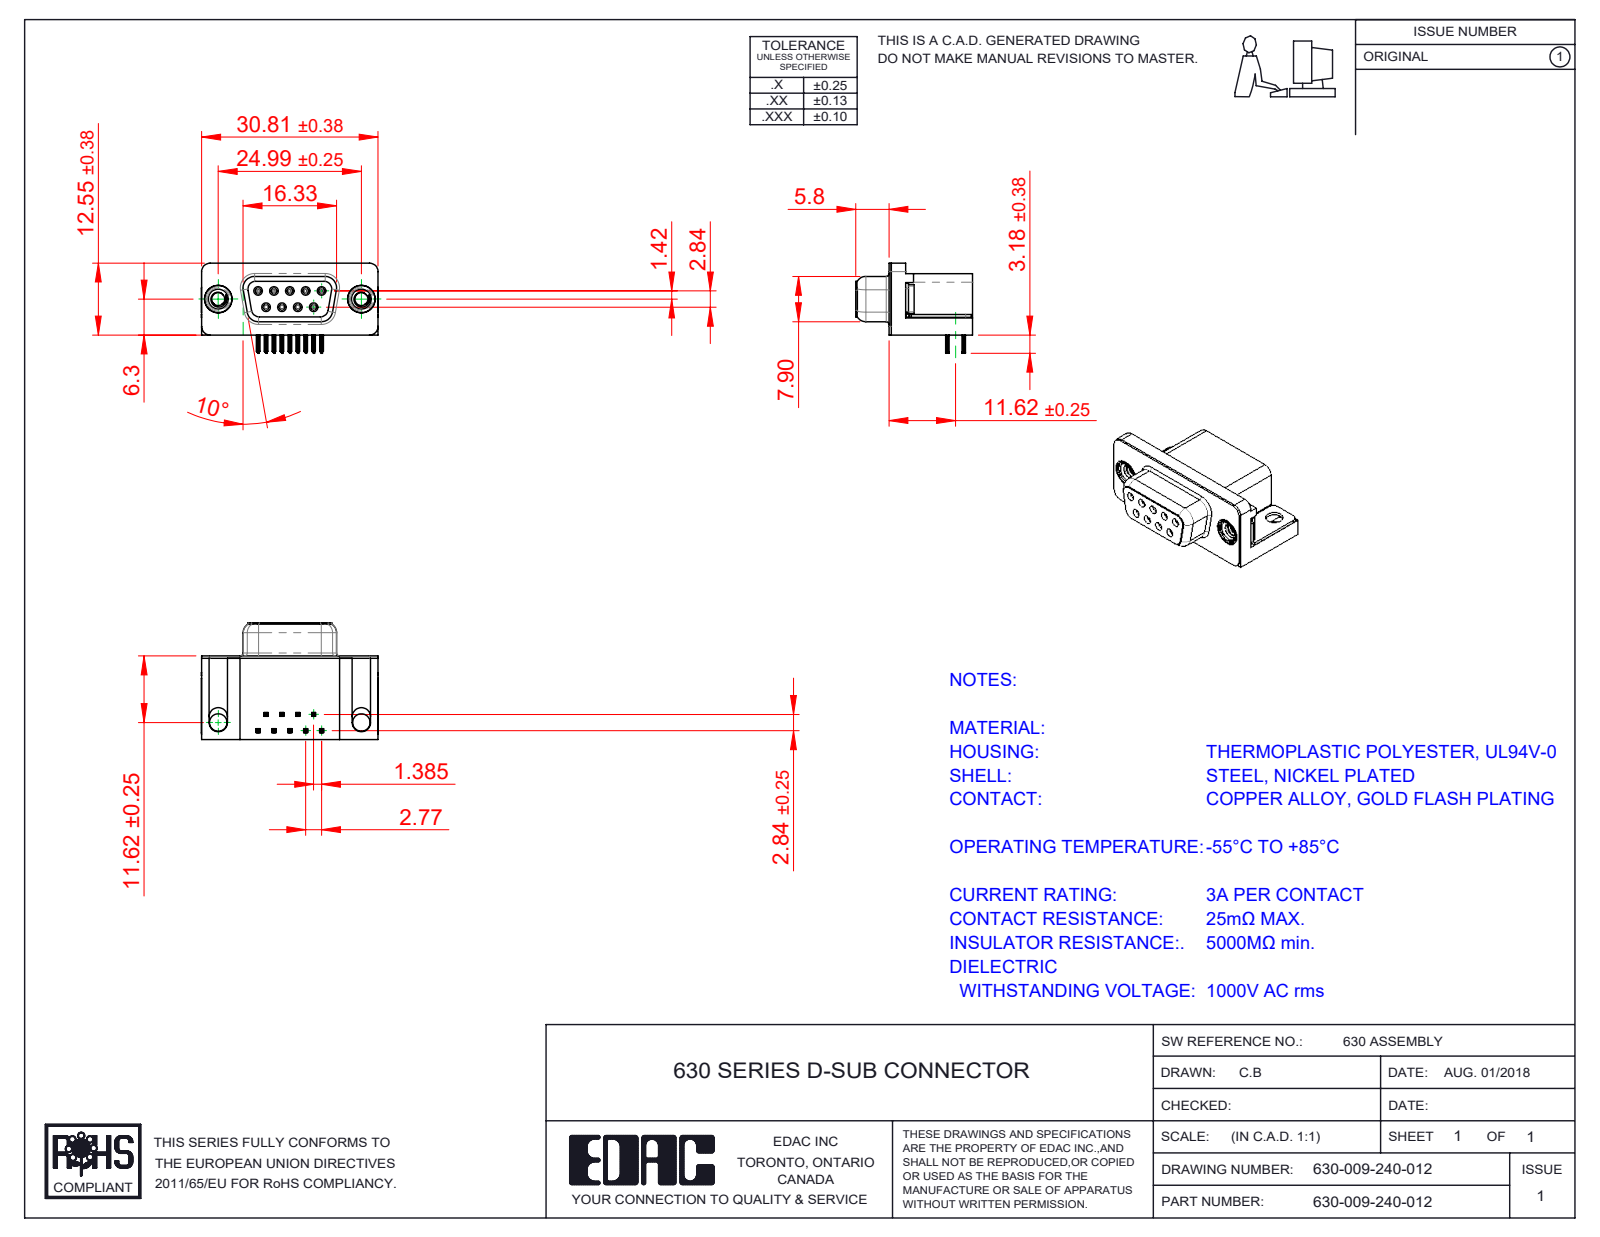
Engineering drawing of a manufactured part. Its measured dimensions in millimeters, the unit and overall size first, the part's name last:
Units: millimetres
Overall size (bounding box): 30.89 × 20.4 × 15.73
Round holes (diameter × count): ⌀0.8 ×9, ⌀0.9 ×9, ⌀2.26 ×2, ⌀3.05 ×2, ⌀4 ×2, ⌀4.8 ×2, ⌀5 ×2
Round bosses / shafts (diameter × count): ⌀1.2 ×9, ⌀4.9 ×2, ⌀4.75 ×2, ⌀3.9 ×2
Partial cylindrical surfaces — rounded edges, fillets, slot ends (radius × count): R0.1 ×72, R0.15 ×36, R0.35 ×18, R1 ×18, R0.34 ×9, R0.25 ×8, R1.35 ×8, R1.6 ×8
Main face-to-face distances: 0.4, 14.6, 14.2, 10.34, 0.5, 6.2, 2.9, 2.5, 11.7, 0.35
Hole centre spacings: 3.16, 2.77, 5.54, 5.03, 5.04, 8.31, 7.48, 7.49
Volume: 4 201 mm³ · Surface area: 5 416 mm²
Bodies: 15 solids, 1570 faces (682 planar, 416 cylindrical, 472 other)
Part name (STEP PRODUCT): 630 Thru Hole Board Mount; 630 Contact Bottom; 630 4-40 Threaded Rivet; 630 Housing_09 Socket (+3 more)
STEP written by: SolidWorks 2020 (CONFIG_CONTROL_DESIGN)
